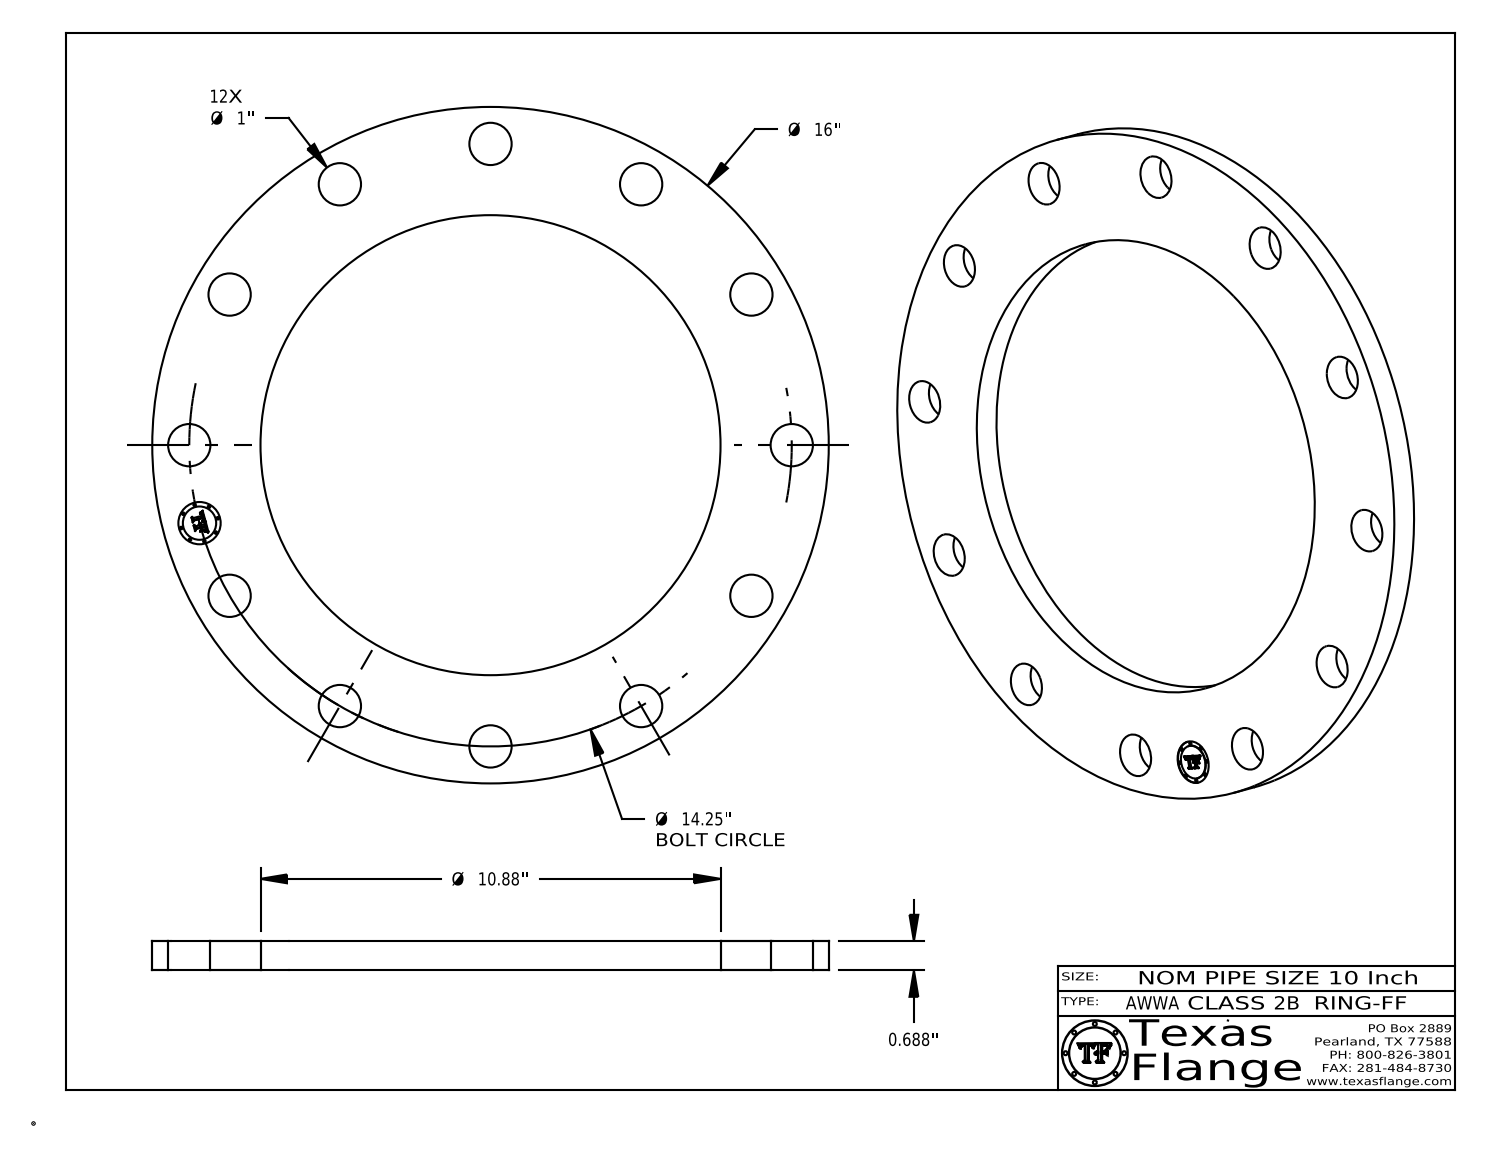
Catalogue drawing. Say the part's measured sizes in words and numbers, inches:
The part is named "AWWA Class 2B-RING-FF". Its 3-D file was written by "CATIA V5 STEP AP214 (AUTOMOTIVE_DESIGN)". It is 1 solid with 415 faces: 367 planar, 48 cylindrical and 0 other. Overall it measures 16 by 16 by 0.688 inches. Its volume is 67.88 cubic inches and its surface area 281.6 square inches. Round holes: 13 of diameter 1, 1 of diameter 10.88. Round bosses or shafts: 8 of diameter 0.061, 1 of diameter 16, 1 of diameter 0.788. The main face-to-face distances are 0.688, 0.673, 0.015, 0.298, 0.292, 0.019, 0.054, 0.194, 0.248, 0.044. The hole center spacings are 7.125, 3.688, 10.076, 12.341, 13.765, 14.25, 11.306, 13.165.
